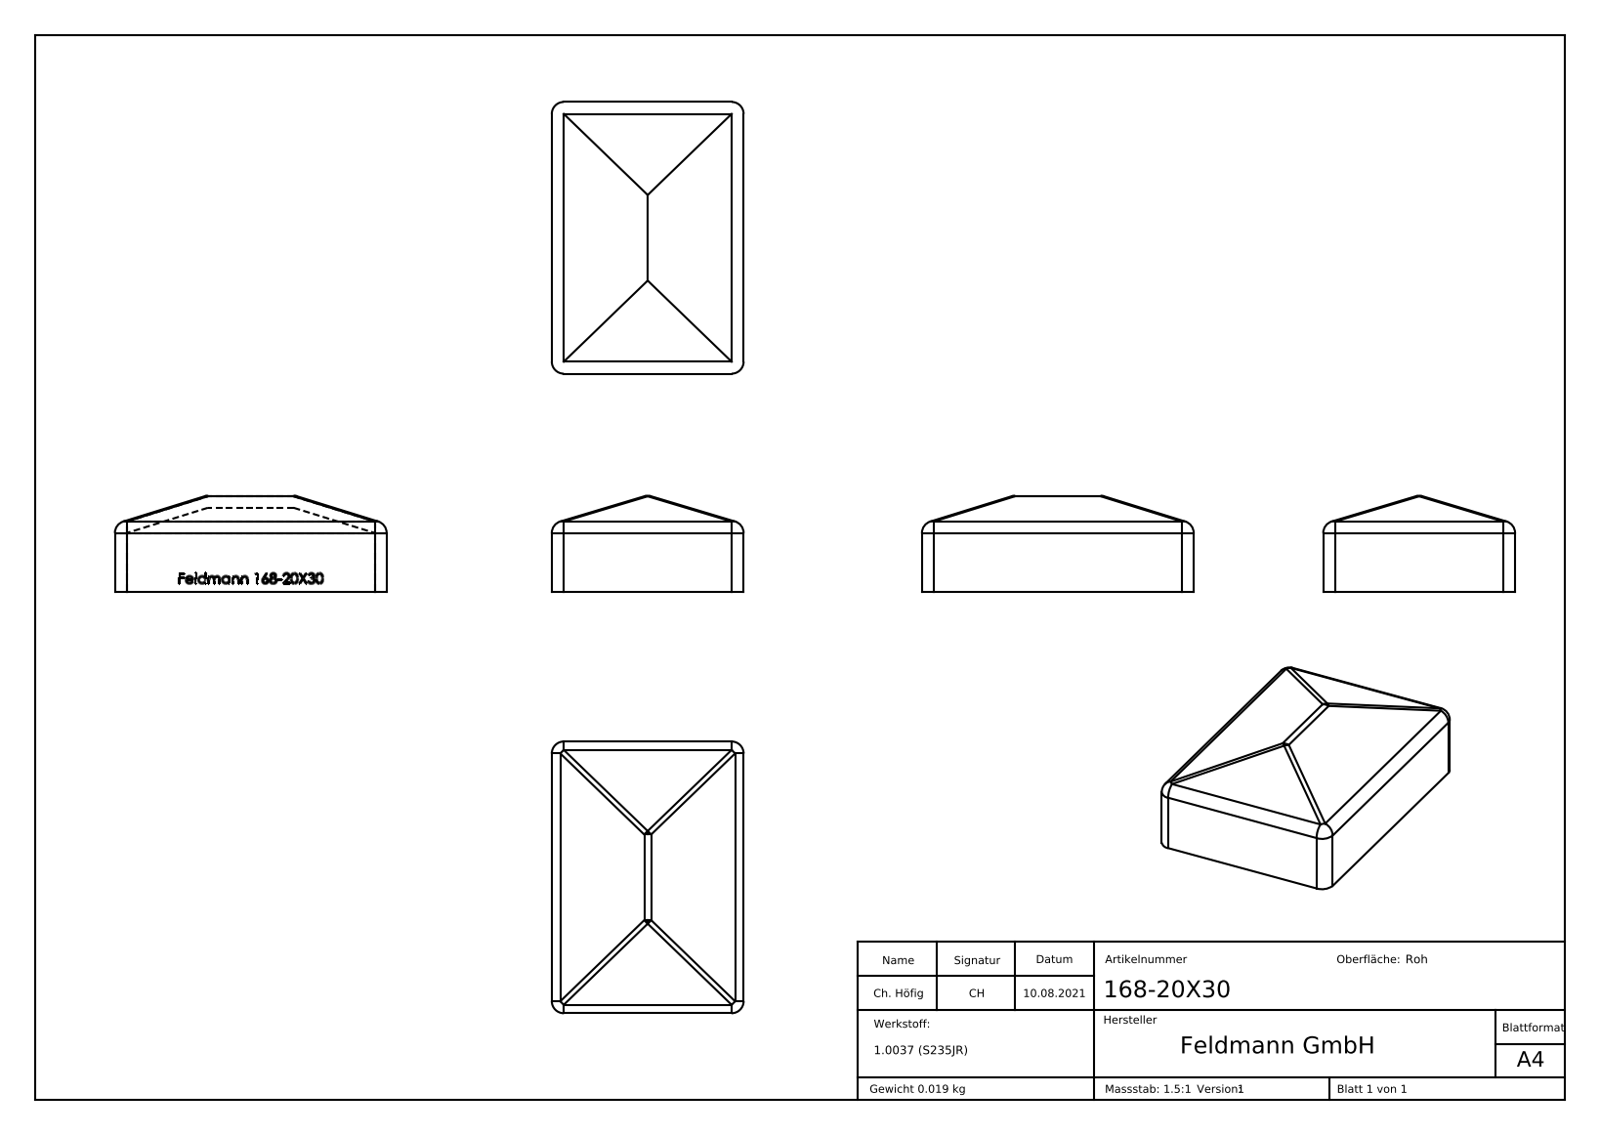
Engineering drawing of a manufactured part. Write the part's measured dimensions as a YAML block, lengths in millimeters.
part_name: "168-20X30"
step_written_by: "SolidWorks 2018 (CONFIG_CONTROL_DESIGN)"
units: millimeters
bodies: {solids: 1, faces: 263, planar: 130, cylindrical: 13, other: 120}
overall_size: [34, 24, 12]
volume: 2410
surface_area: 3391
partial_cylinders:
  - {radius: 1.5, count: 13}
face_to_face_distances: [1.5, 22.5, 32.5, 24, 21, 34, 31, 1.4, 21.1, 22.6]
